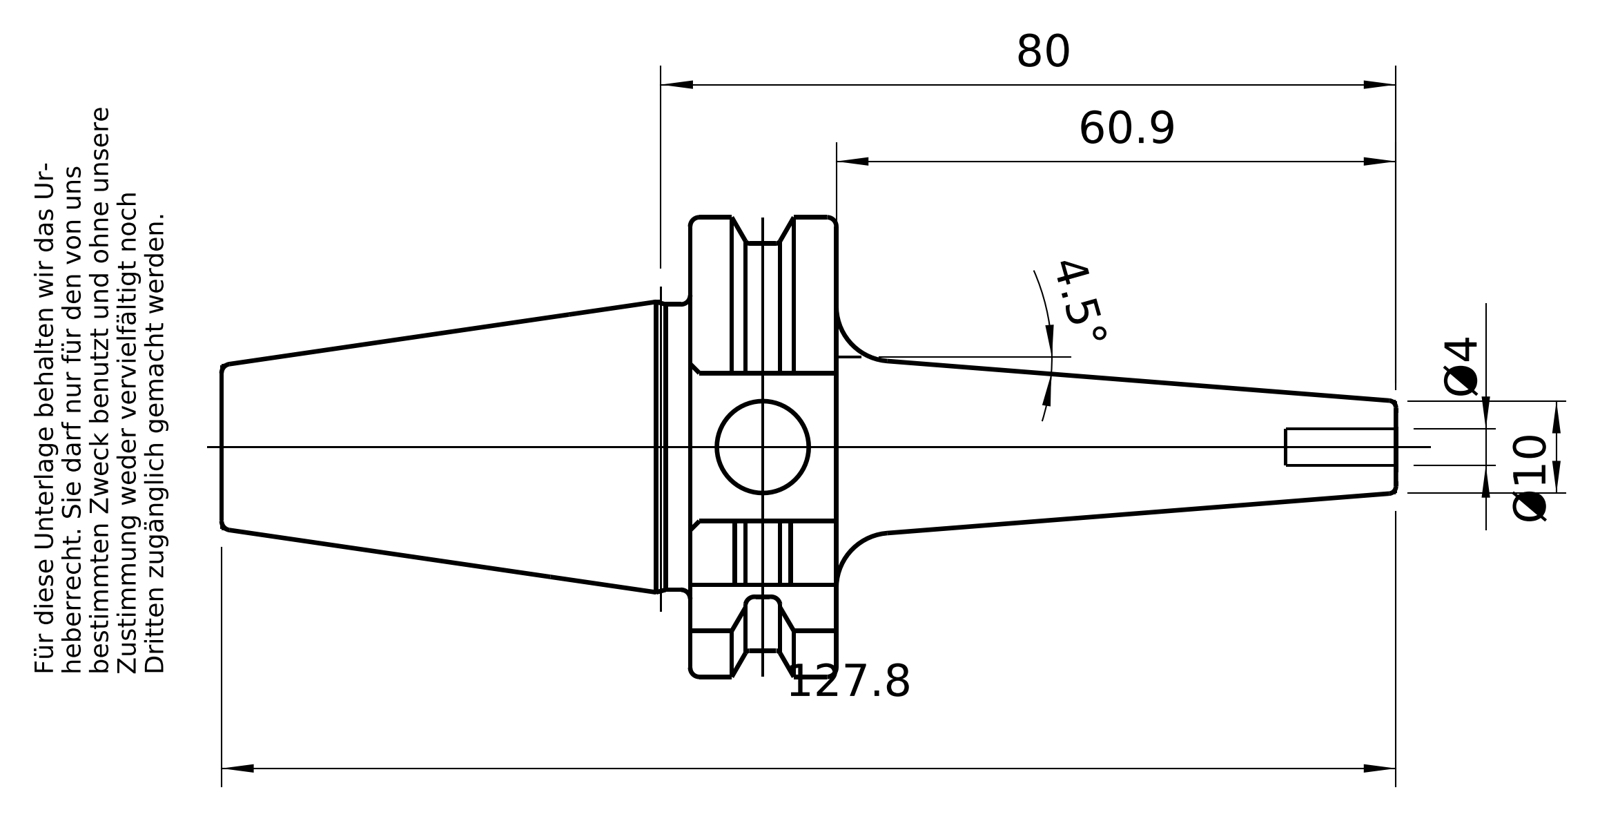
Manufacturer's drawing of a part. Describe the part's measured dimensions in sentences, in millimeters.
The part is named "30-440-04". Its 3-D file was written by "PRO/ENGINEER BY PARAMETRIC TECHNOLOGY CORPORATION, 2010430 (CONFIG_CONTROL_DESIGN)". It is 1 solid with 90 faces: 21 planar, 21 cylindrical and 48 other. Overall it measures 127.65 by 49.98 by 47.32 millimeters. Its volume is 59 543 cubic millimeters and its surface area 14 532 square millimeters. Round holes: 1 of diameter 4, 1 of diameter 10.11, 1 of diameter 13.01, 1 of diameter 13.5. Round bosses or shafts: 1 of diameter 31.05, 1 of diameter 12.01. Partial cylindrical surfaces (rounded edges, fillets, slot ends): 1 of radius 22.02, 1 of radius 24.99. The main face-to-face distances are 15.85, 35.1, 16.1, 6.95, 23.05, 3.8, 31.3, 50.85, 66.7, 60.95.
